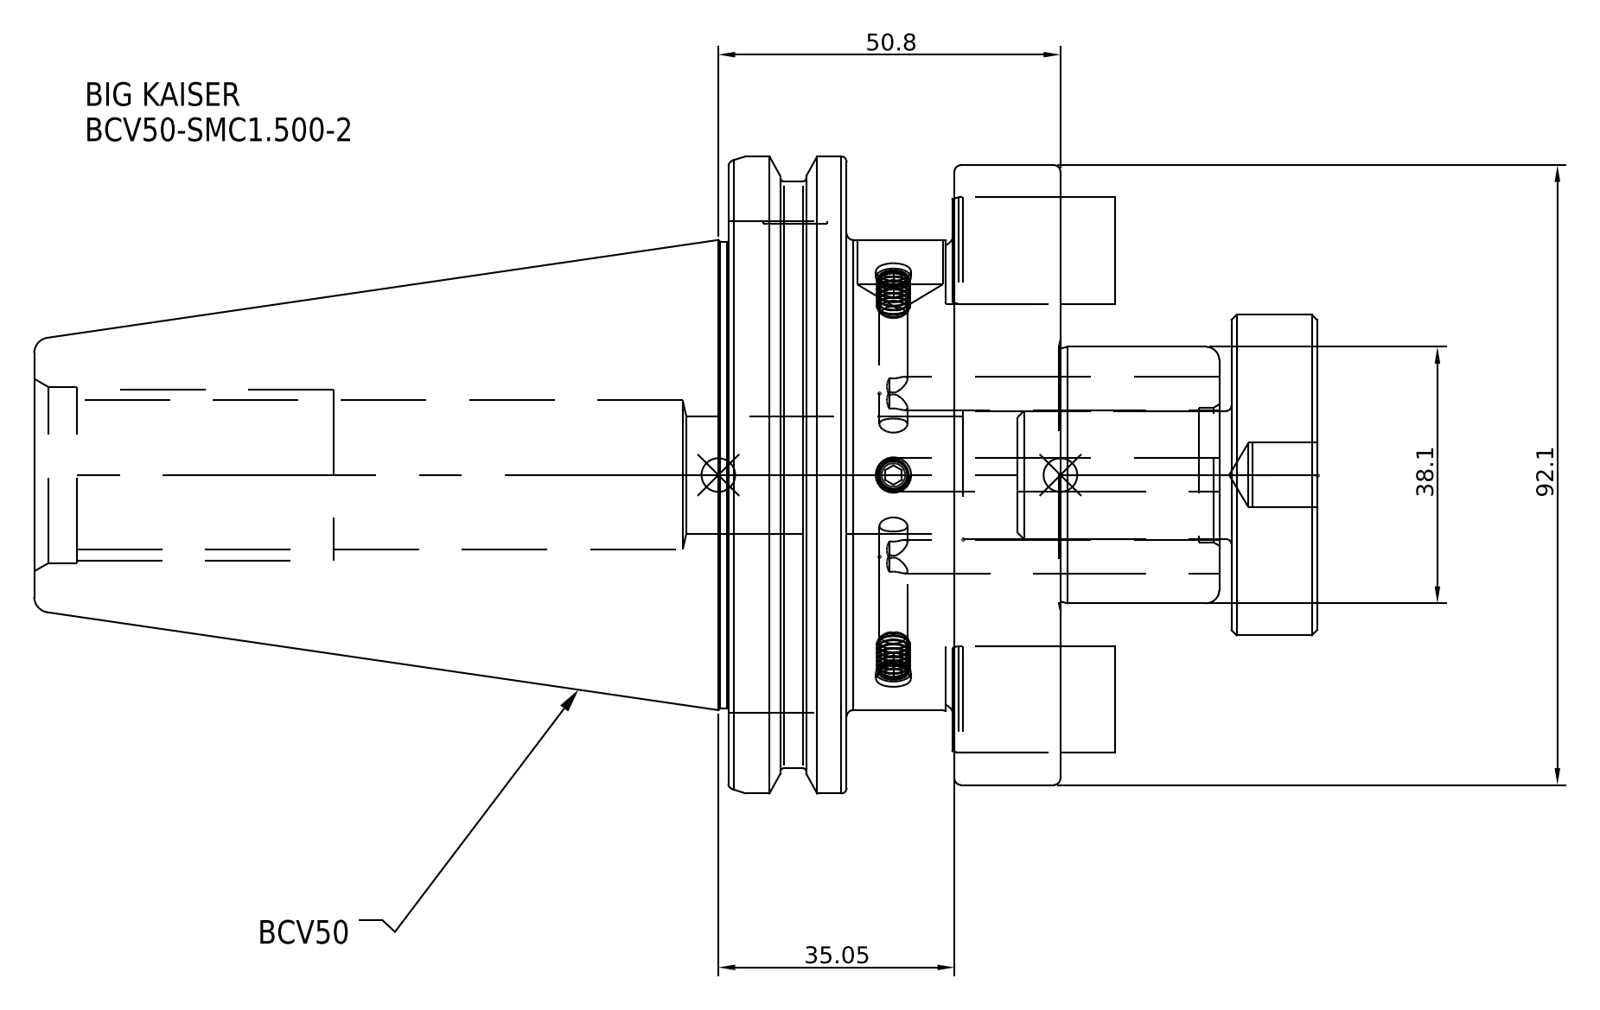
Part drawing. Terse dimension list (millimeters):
name: BCV50-SMC1_500-2
written by: SolidWorks 2021 (CONFIG_CONTROL_DESIGN)
unit: mm
bodies: 1 solid, 38 faces (18 planar, 14 cylindrical, 6 other)
size: 160.48 × 98.43 × 98.43
volume: 547 902 mm³; area: 53 092 mm²
holes: 1× ⌀17.46
bosses: 1× ⌀98.43, 1× ⌀92.1, 1× ⌀91.29, 1× ⌀69.85
face distances: 49.3, 31.75, 17.55, 15.75, 16, 33.55, 152.4, 136.65, 120.65, 103.1
